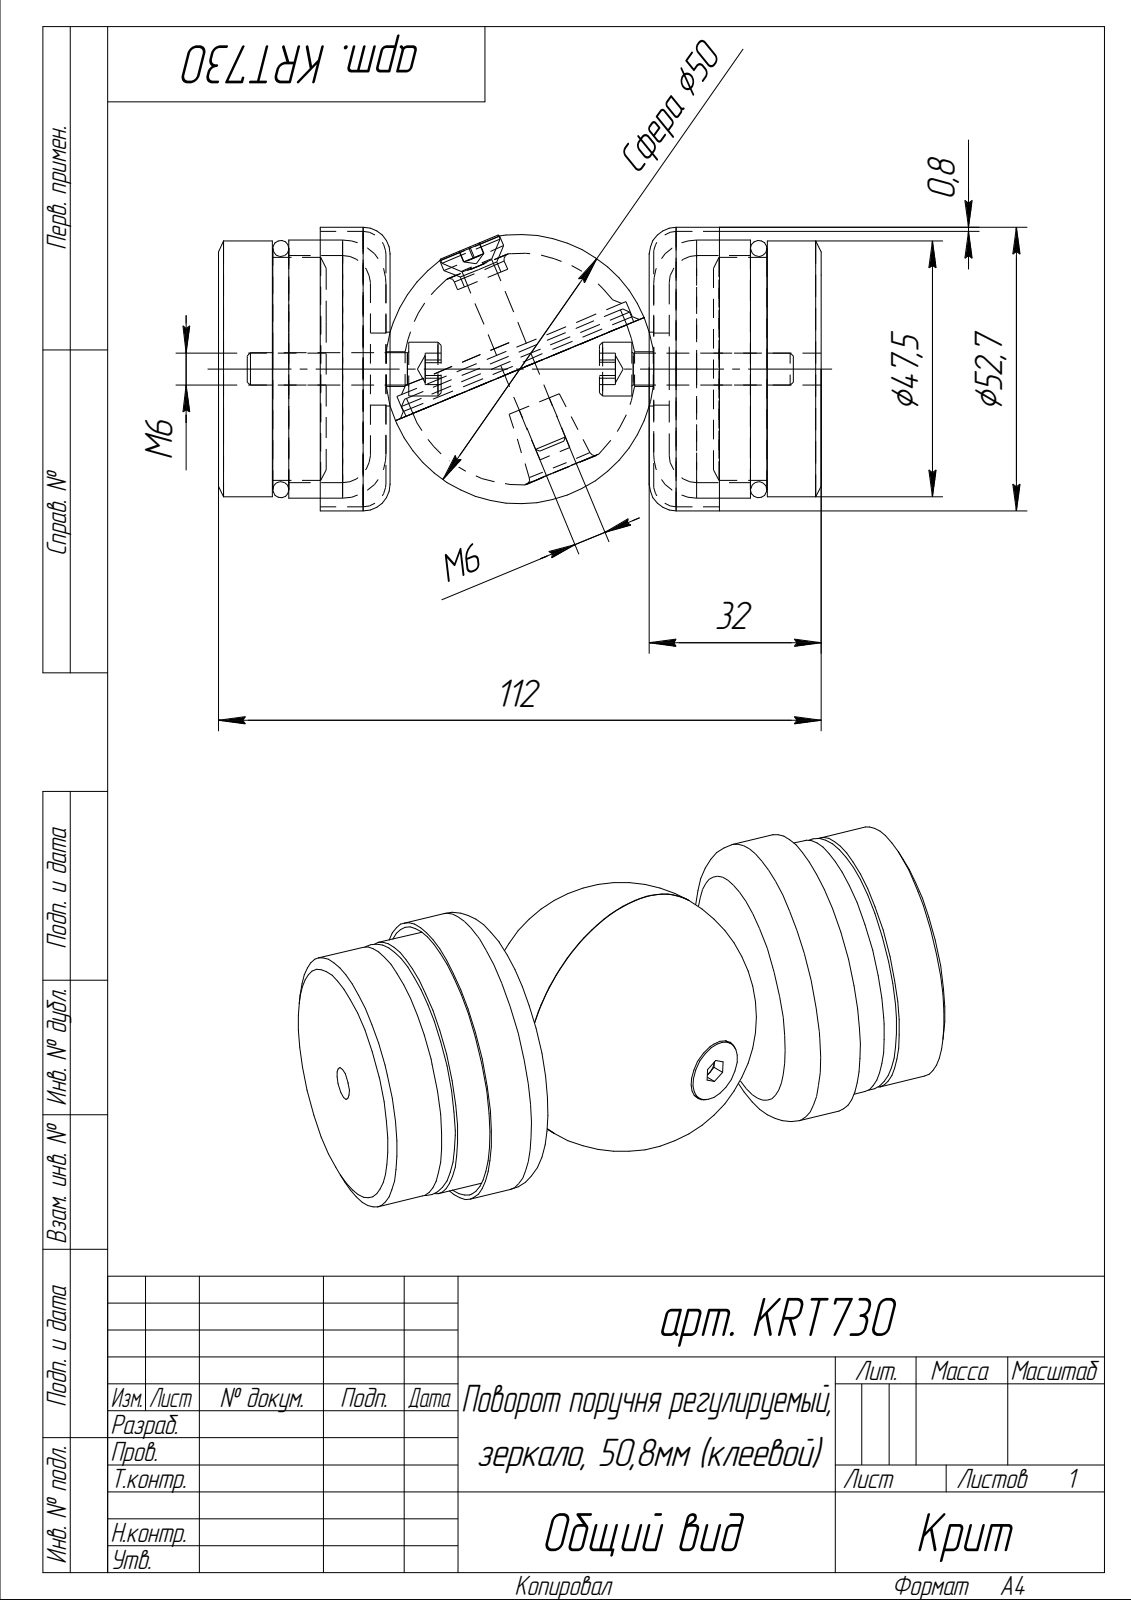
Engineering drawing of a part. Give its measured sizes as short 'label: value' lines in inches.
name: арт. KRT730; socket head cap screw_am_B18.3.1M - 6 x 1.0 x 30 Hex SHCS -- 30NHX; арт. KRT730.004; арт. KRT730.005 (+6 more)
written by: SolidWorks 2014 (AUTOMOTIVE_DESIGN)
unit: in
bodies: 13 solids, 213 faces (69 planar, 66 cylindrical, 78 other)
size: 4.725 × 3.383 × 2.075
volume: 7.068 in³; area: 99.57 in²
holes: 3× ⌀0.236, 2× ⌀0.252, 2× ⌀0.528, 2× ⌀0.539, 2× ⌀1.657, 2× ⌀2.012, 1× ⌀0.291, 1× ⌀0.472, 1× ⌀1.693, 1× ⌀1.811
bosses: 3× ⌀0.394, 2× ⌀2.075, 2× ⌀1.886, 2× ⌀1.87, 2× ⌀1.63, 2× ⌀0.236, 1× ⌀1.803, 1× ⌀0.461
face distances: 1.225, 3.181, 1.256, 3.15, 0.031, 1.925, 0.788, 3.619, 0.437, 0.469
